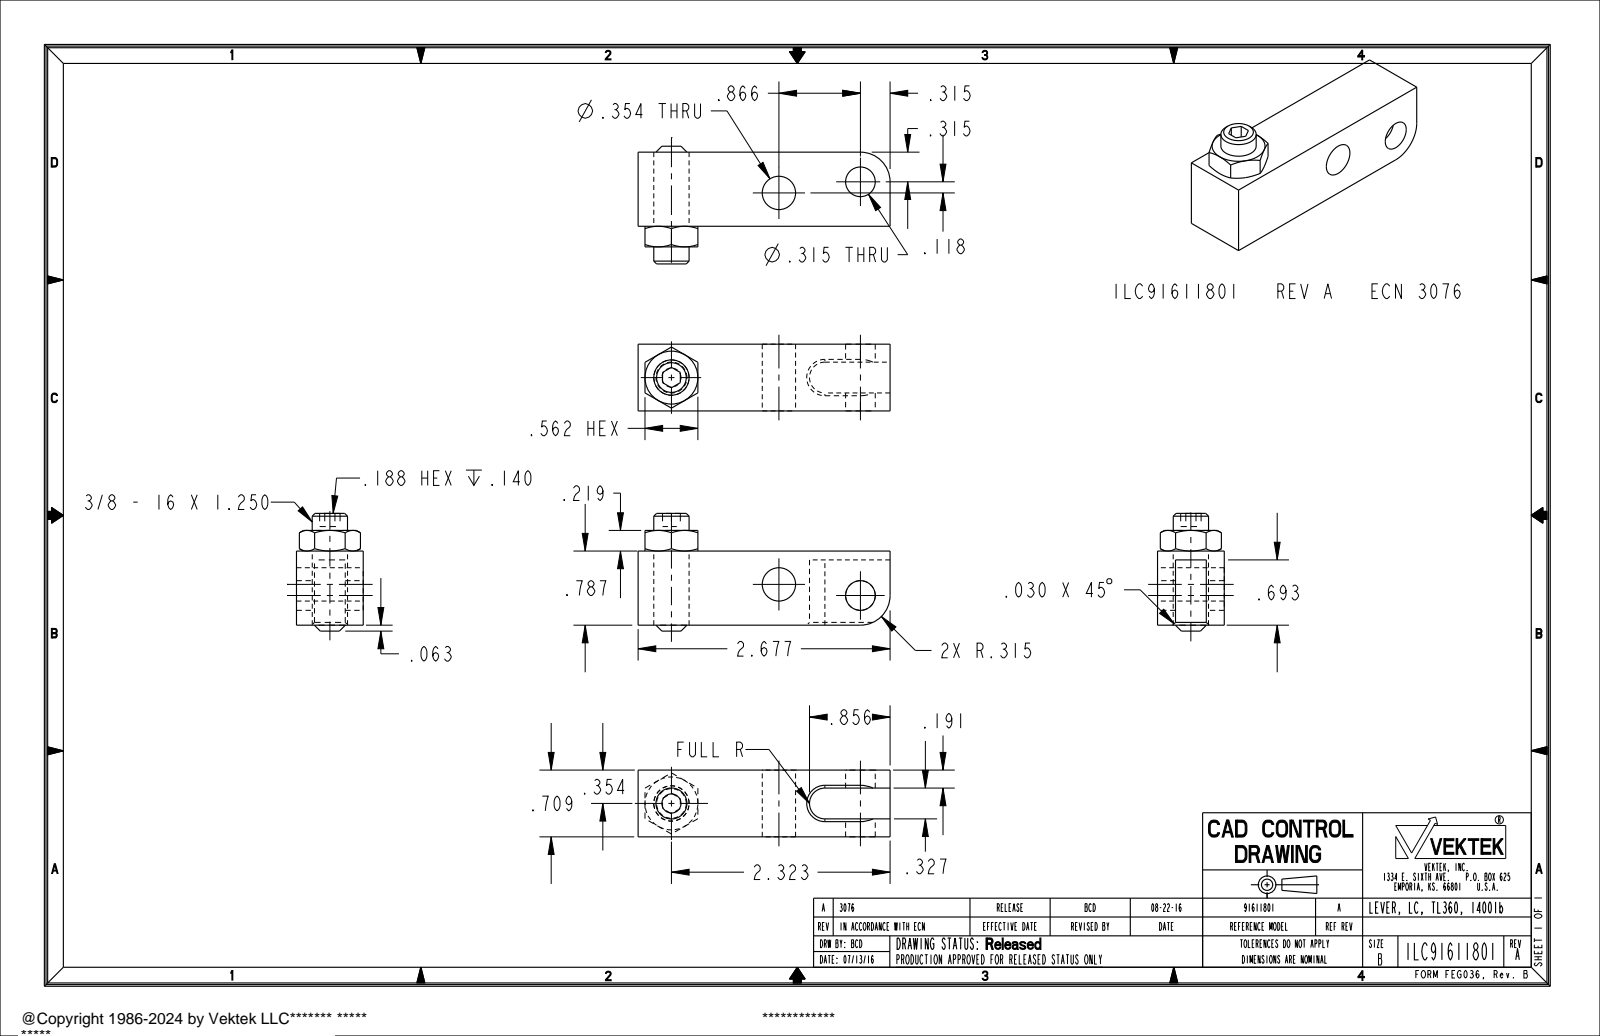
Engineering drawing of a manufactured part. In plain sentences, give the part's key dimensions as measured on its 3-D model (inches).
The part is named "ILC91611801". Its 3-D file was written by "PRO/ENGINEER BY PARAMETRIC TECHNOLOGY CORPORATION, 2013320 (AUTOMOTIVE_DESIGN)". It is 1 solid with 57 faces: 27 planar, 13 cylindrical and 17 other. Overall it measures 2.677 by 1.25 by 0.709 inches. Its volume is 1.278 cubic inches and its surface area 12.39 square inches. Round holes: 1 of diameter 0.315, 1 of diameter 0.354. Round bosses or shafts: 2 of diameter 0.375. Partial cylindrical surfaces (rounded edges, fillets, slot ends): 1 of radius 0.164, 1 of radius 0.315. The main face-to-face distances are 0.709, 0.787, 0.191, 0.518, 0.327, 0.693, 0.094, 2.677, 1.006, 0.313. The hole center spacings are 0.874.
